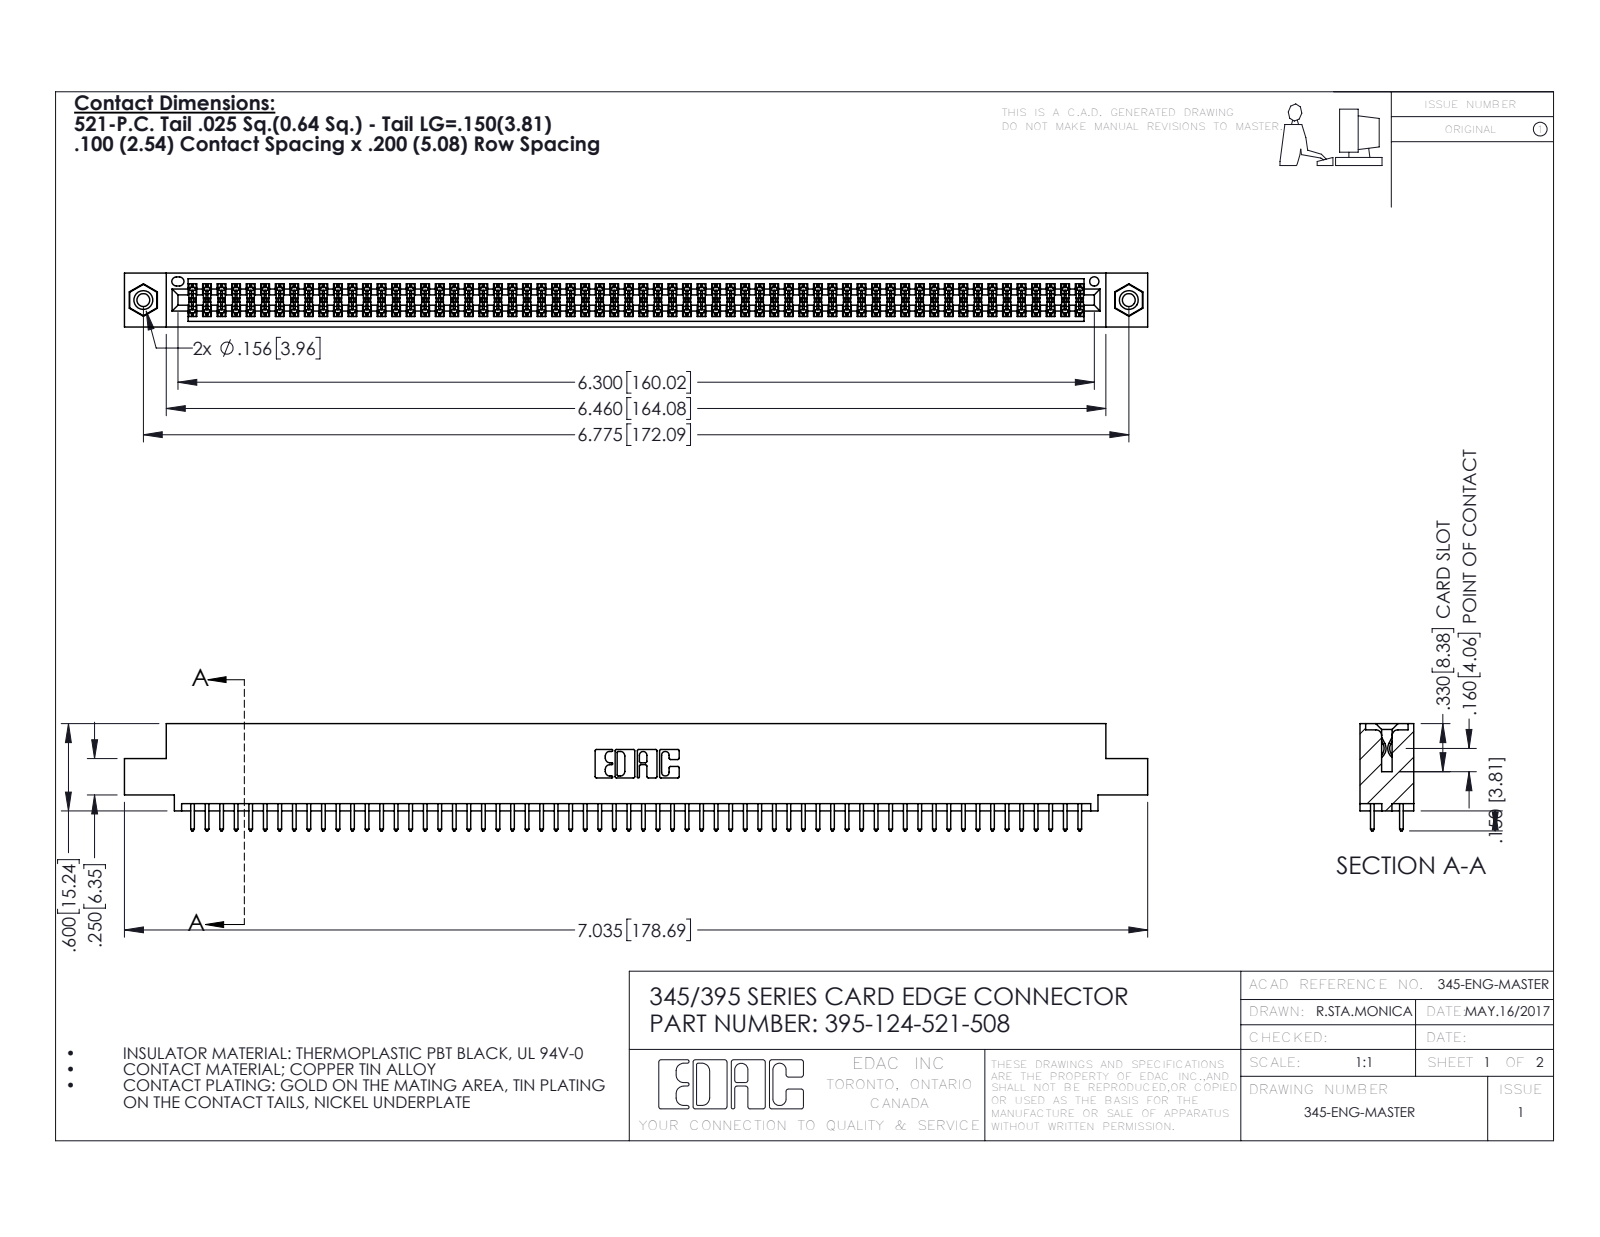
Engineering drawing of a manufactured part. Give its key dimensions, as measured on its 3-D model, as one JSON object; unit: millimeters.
{"part_name": "395-124-521-508; 345-292-001_345-293-121; 345 Part_0.110 Offset - 0.156 Dia-TI; 345-250-001_345-250-003-102", "step_written_by": "SolidWorks 2016 (CONFIG_CONTROL_DESIGN)", "units": "millimeters", "bodies": {"solids": 127, "faces": 6390, "planar": 4208, "cylindrical": 2166, "other": 16}, "overall_size": [178.7, 18.7, 9.4], "volume_mm3": 17420, "surface_area_mm2": 25900, "round_holes": [[2.3, 2], [3.2, 2], [4, 2], [1.6, 1]], "round_bosses_or_shafts": [[3.9, 2]], "partial_cylinders_radius": [[0.2, 186], [0.3, 124], [0.3, 22], [0.2, 6], [0.8, 6], [0.7, 3], [0.4, 2], [0.5, 2]], "face_to_face_distances": [1.8, 7.6, 5.1, 2.5, 6.9, 0.6, 9.4, 5.7, 4.4, 3.8], "hole_center_spacings": [6.9, 166.1, 172.1]}
